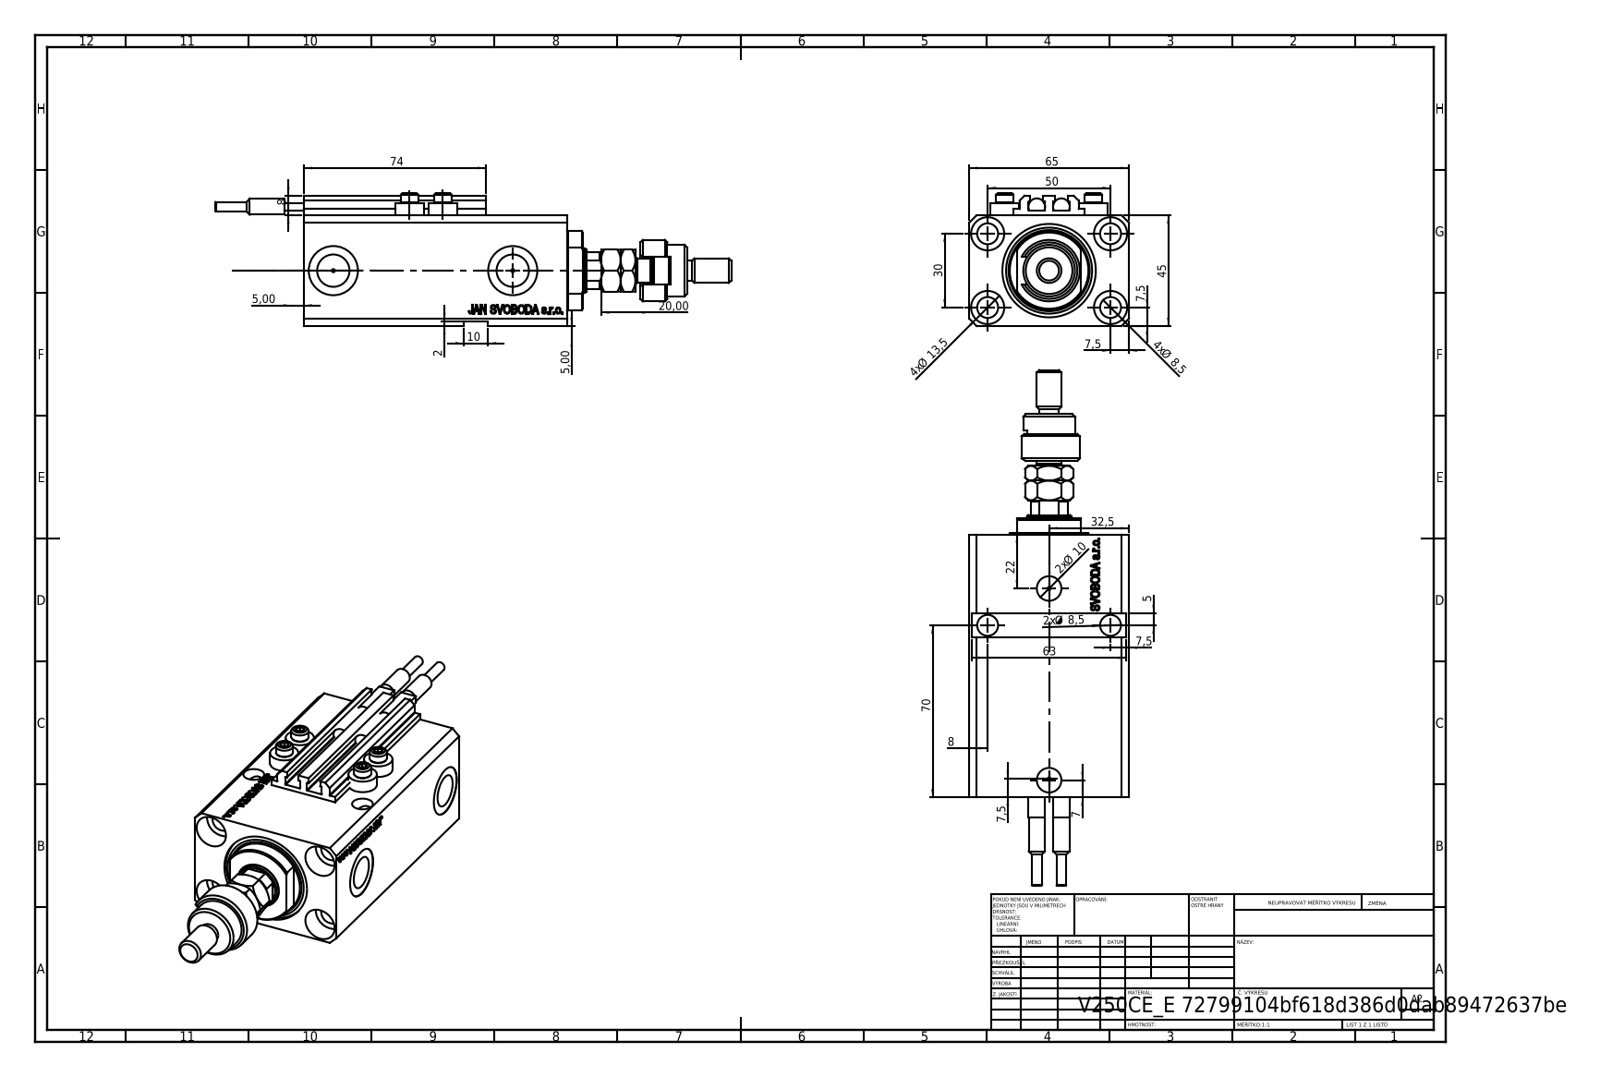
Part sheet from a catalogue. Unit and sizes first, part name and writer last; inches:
Units: inches
Overall size (bounding box): 8.264 × 2.559 × 2.126
Round holes (diameter × count): ⌀0.335 ×7, ⌀0.049 ×4, ⌀0.157 ×4, ⌀0.531 ×4, ⌀0.394 ×2, ⌀0.518 ×2, ⌀0.787 ×2, ⌀0.709 ×1, ⌀1.496 ×1
Round bosses / shafts (diameter × count): ⌀0.457 ×4, ⌀0.276 ×4, ⌀0.268 ×2, ⌀0.256 ×2, ⌀0.157 ×2, ⌀0.984 ×1, ⌀0.827 ×1, ⌀0.63 ×1
Partial cylindrical surfaces — rounded edges, fillets, slot ends (radius × count): R0.008 ×10, R0.217 ×1, R0.335 ×1, R0.344 ×1, R0.63 ×1
Main face-to-face distances: 1.772, 2.559, 0.079, 3.224, 1.85, 0.118, 0.988, 4.213, 2.953, 0.394
Hole centre spacings: 1.148, 1.969, 0.535, 0.595, 1.098, 1.181, 1.324, 1.417
Volume: 17.61 in³ · Surface area: 135.3 in²
Bodies: 12 solids, 1220 faces (575 planar, 163 cylindrical, 482 other)
Part name (STEP PRODUCT): V250CE_E_Body; V250CE_VC_E; FEMALE_PART_FOR_DFA; V250CE_C_VCP (+3 more)
STEP written by: SolidWorks 2019 (CONFIG_CONTROL_DESIGN)
